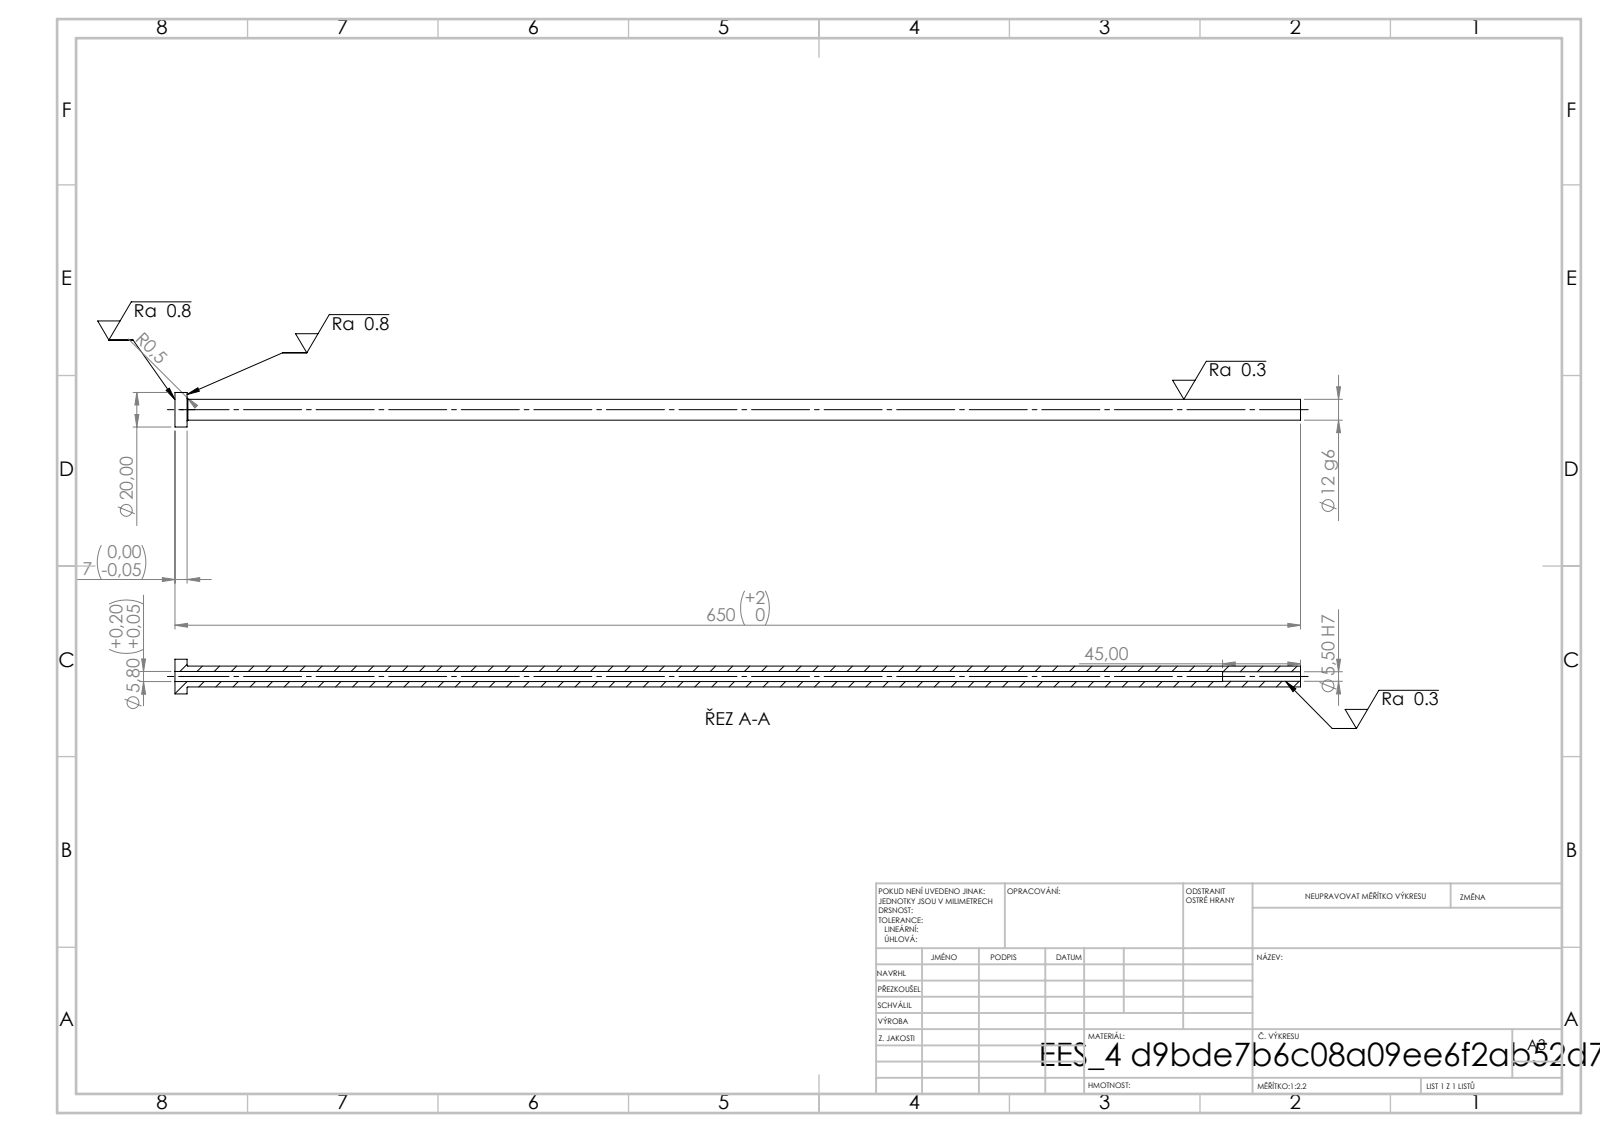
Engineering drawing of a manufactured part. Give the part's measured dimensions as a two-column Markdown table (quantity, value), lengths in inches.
| quantity | value |
| --- | --- |
| STEP written by | SolidWorks 2019 (CONFIG_CONTROL_DESIGN) |
| units | inches |
| bodies | 1 solid, 14 faces (4 planar, 8 cylindrical, 2 other) |
| overall size | 25.591 × 0.787 × 0.787 |
| volume | 3.531 in³ |
| surface area | 57.44 in² |
| round holes (diameter × count) | 0.217 × 1, 0.228 × 1 |
| round bosses / shafts (diameter × count) | 0.787 × 1, 0.472 × 1 |
| main face-to-face distances | 0.276, 25.591, 25.315, 23.819, 23.543, 1.772 |
